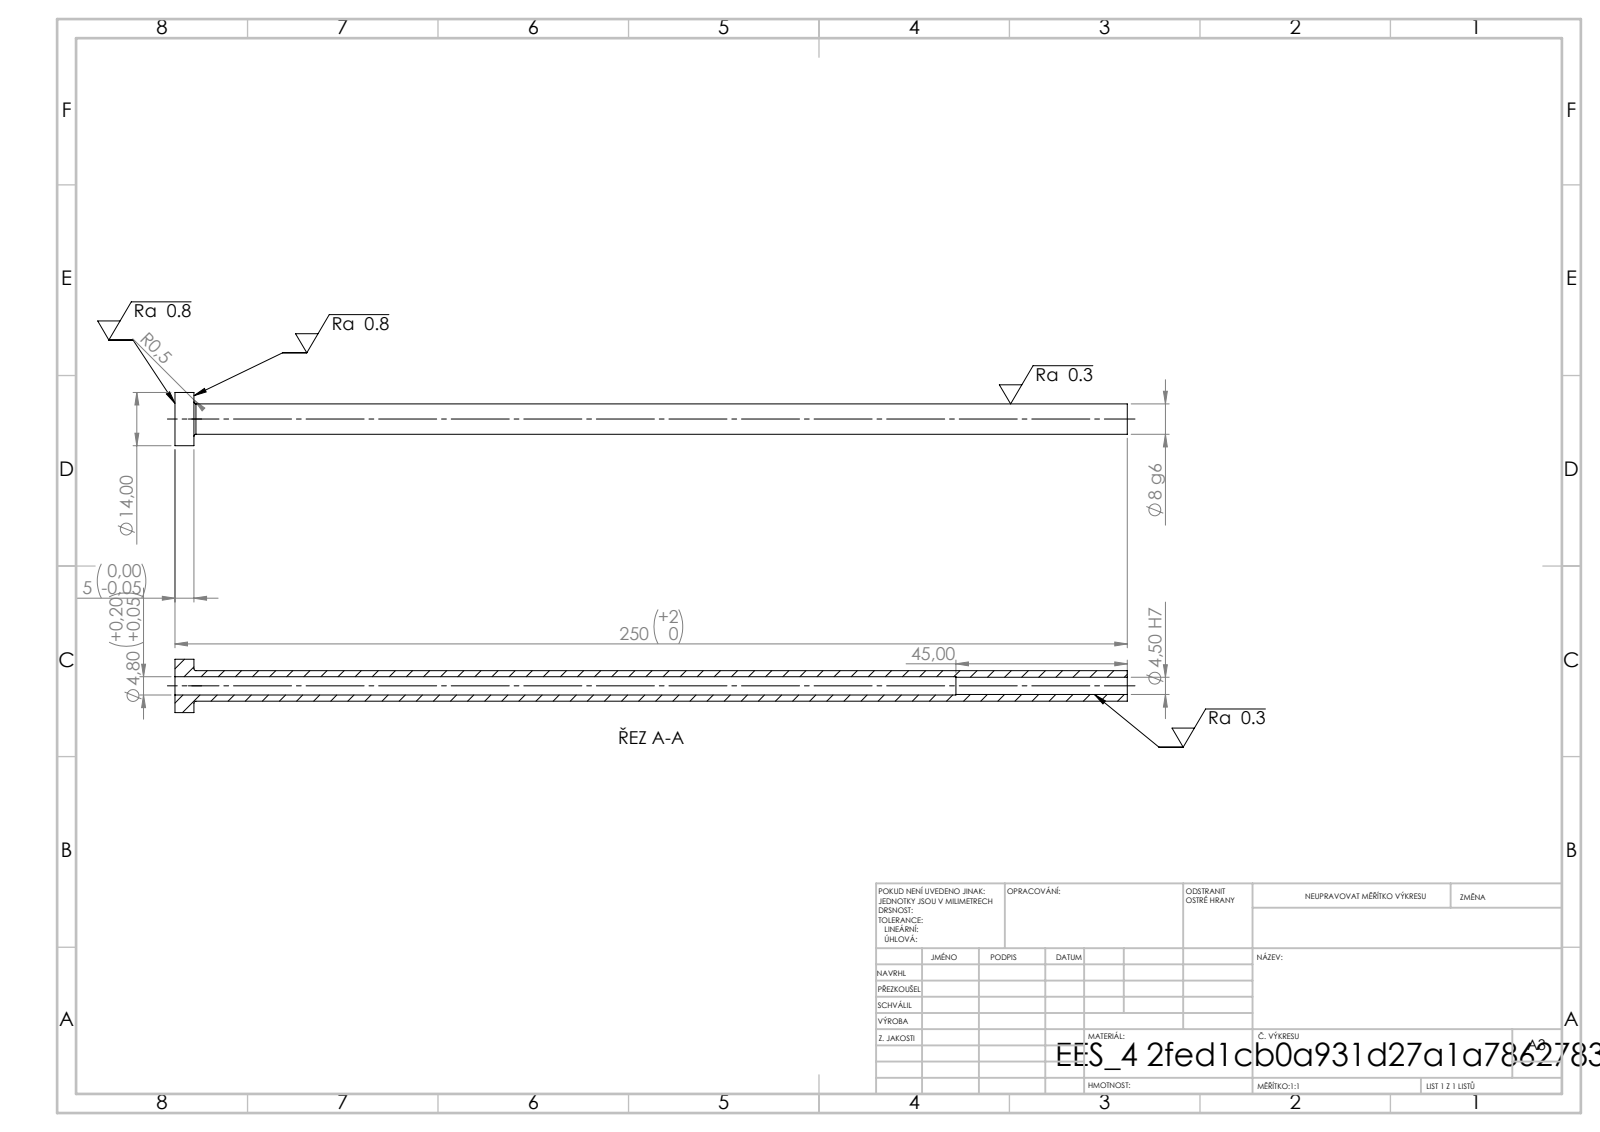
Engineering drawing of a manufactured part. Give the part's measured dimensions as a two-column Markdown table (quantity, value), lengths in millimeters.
| quantity | value |
| --- | --- |
| STEP written by | SolidWorks 2019 (CONFIG_CONTROL_DESIGN) |
| units | millimeters |
| bodies | 1 solid, 14 faces (4 planar, 8 cylindrical, 2 other) |
| overall size | 250 × 14 × 14 |
| volume | 8 661 mm³ |
| surface area | 10 376 mm² |
| round holes (diameter × count) | 4.5 × 1, 4.8 × 1 |
| round bosses / shafts (diameter × count) | 14 × 1, 8 × 1 |
| main face-to-face distances | 5, 250, 245, 205, 200, 45 |
